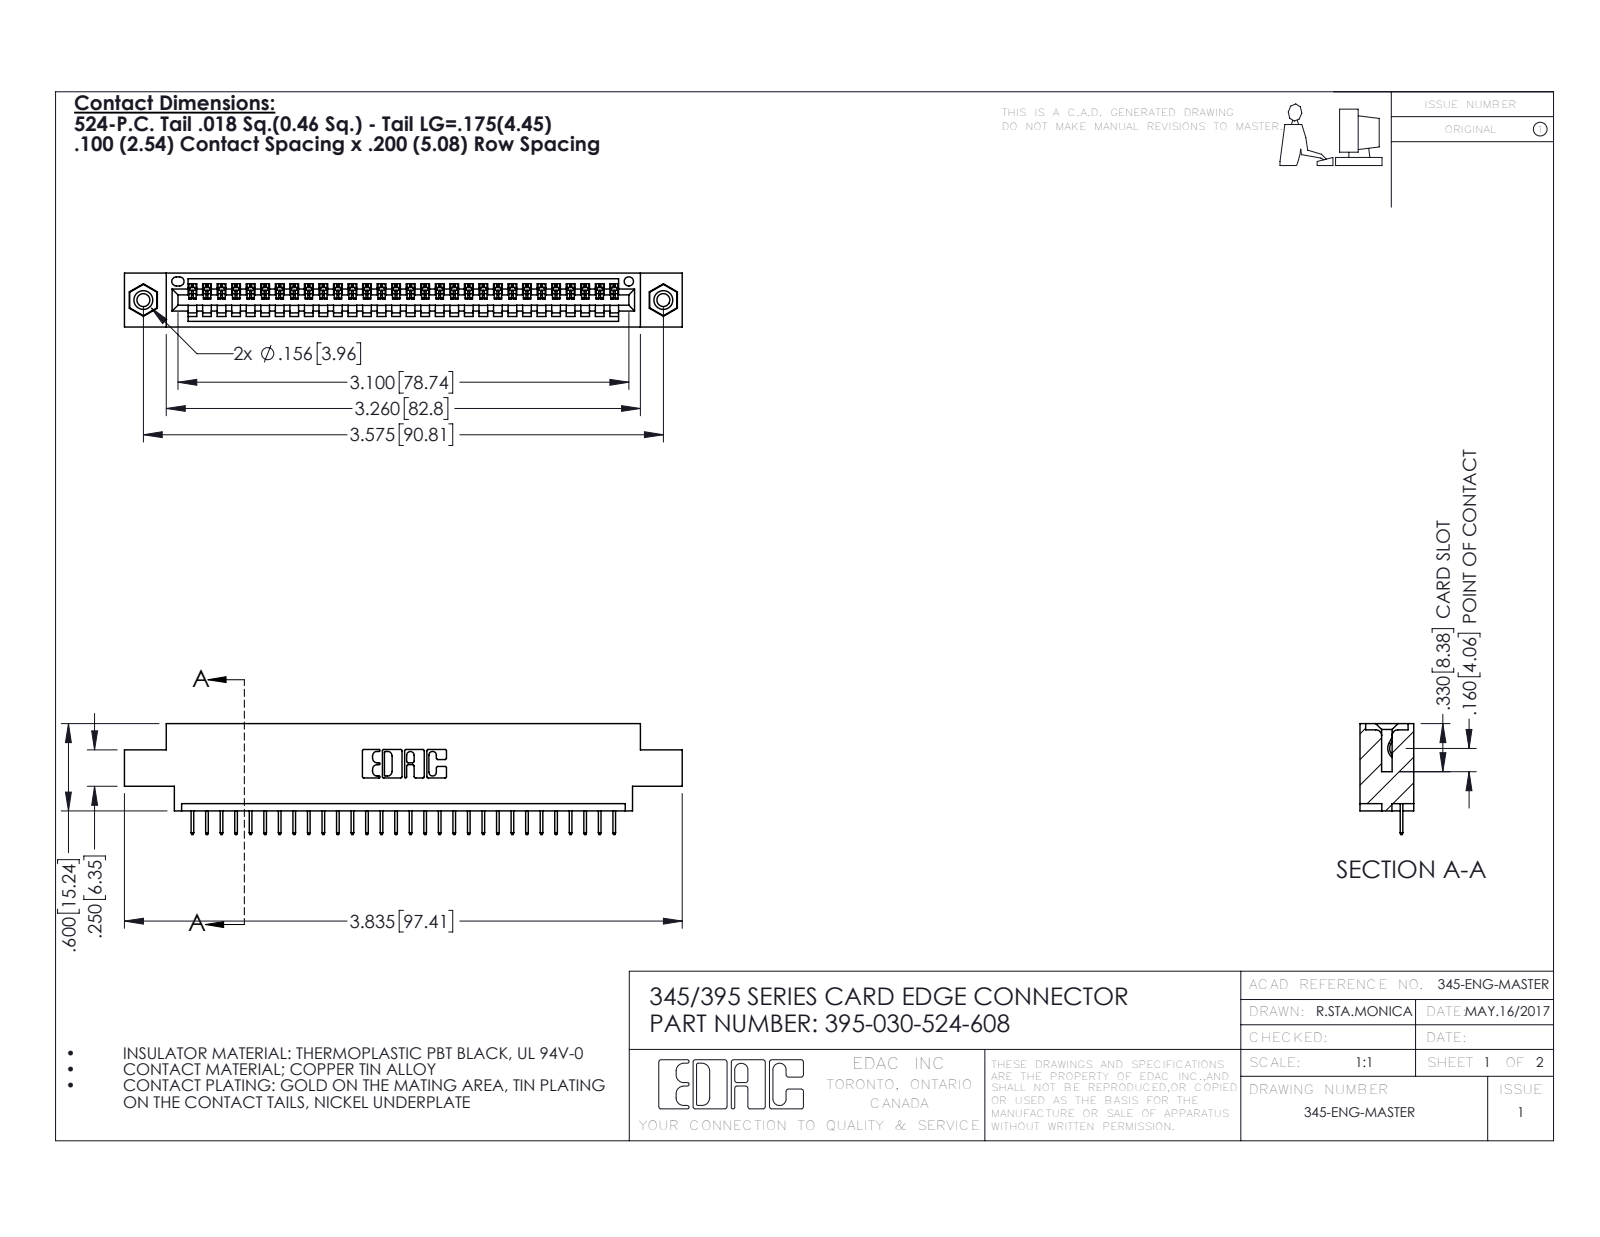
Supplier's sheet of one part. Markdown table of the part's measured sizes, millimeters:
| quantity | value |
| --- | --- |
| part name | 345-250-001_345-250-003-102; 345 Part_0.170 Offset - 0.156 Dia-TI; 345-292-001_345-293-124; 395-030-524-608 |
| STEP written by | SolidWorks 2016 (CONFIG_CONTROL_DESIGN) |
| units | millimeters |
| bodies | 33 solids, 2050 faces (1496 planar, 538 cylindrical, 16 other) |
| overall size | 97.4 × 19.4 × 9.4 |
| volume | 8 910 mm³ |
| surface area | 11 450 mm² |
| round holes (diameter × count) | 2.3 × 2, 3.2 × 2, 4 × 2, 1.6 × 1 |
| round bosses / shafts (diameter × count) | 3.9 × 2 |
| partial cylindrical surfaces (radius × count) | 0.2 × 60, 0.3 × 22, 0.2 × 6, 0.8 × 6, 0.7 × 3, 0.8 × 2, 1 × 2, 0.4 × 1 |
| main face-to-face distances | 1.8, 7.6, 9.4, 5.1, 2.5, 6.9, 0.6, 5.7, 1.8, 4.4 |
| hole center spacings | 6.9, 84.8, 90.8 |
